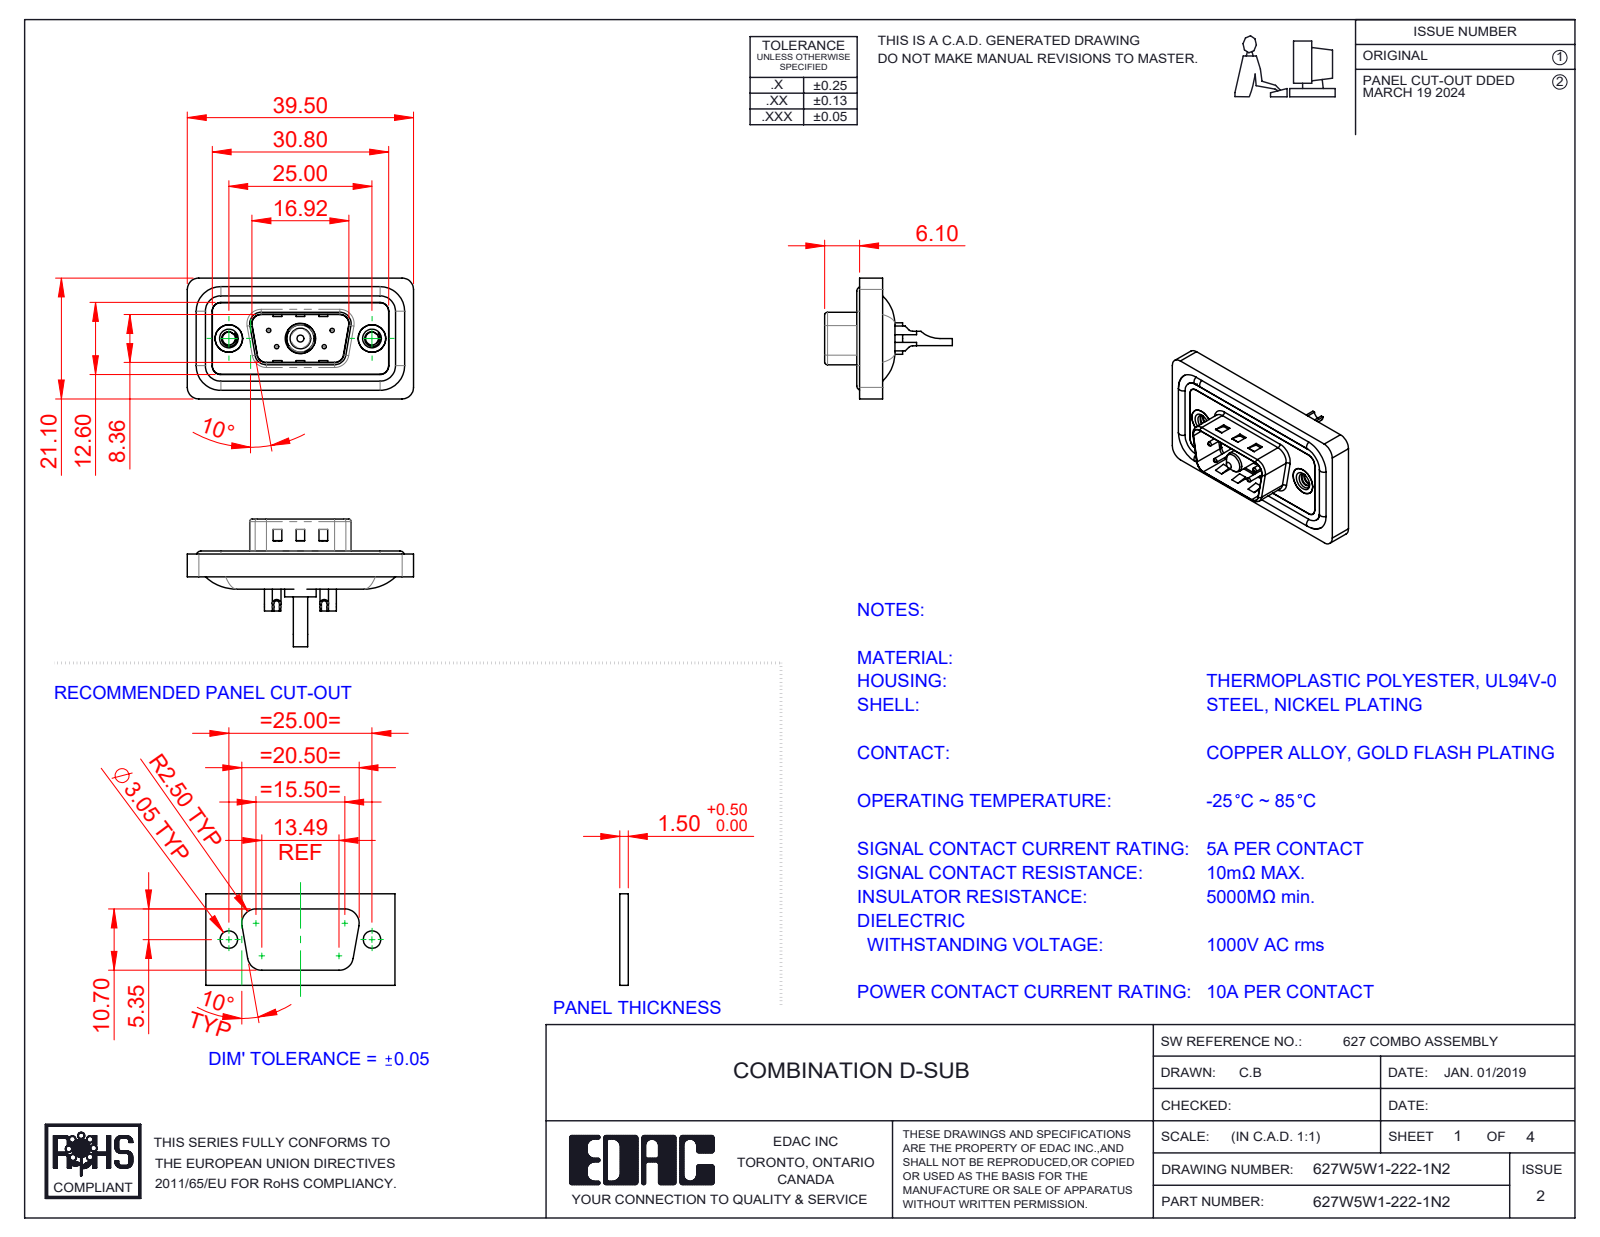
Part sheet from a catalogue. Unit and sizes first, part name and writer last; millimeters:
Units: millimetres
Overall size (bounding box): 39.5 × 22.3 × 21.1
Round holes (diameter × count): ⌀0.75 ×4, ⌀1 ×4, ⌀1.6 ×4, ⌀2 ×4, ⌀2.26 ×2, ⌀4 ×2, ⌀4.8 ×2, ⌀5 ×2, ⌀1.7 ×1, ⌀4.85 ×1, ⌀5.3 ×1
Round bosses / shafts (diameter × count): ⌀1.6 ×4, ⌀1.5 ×4, ⌀4.9 ×2, ⌀5.5 ×1, ⌀5.2 ×1, ⌀4.75 ×1, ⌀3.75 ×1, ⌀3.6 ×1
Partial cylindrical surfaces — rounded edges, fillets, slot ends (radius × count): R1.5 ×22, R2 ×18, R0.5 ×8, R1.6 ×8, R1 ×6, R0.25 ×4, R0.6 ×4, R0.65 ×4
Main face-to-face distances: 0.4, 1.1, 2.9, 1.6, 1.5, 3.1, 0.5, 2.5, 4, 0.8
Hole centre spacings: 3.16, 5.72, 7.1, 12.5, 18.1, 4.39, 4.4, 8.31
Volume: 4 391 mm³ · Surface area: 7 021 mm²
Bodies: 13 solids, 604 faces (193 planar, 266 cylindrical, 145 other)
Part name (STEP PRODUCT): 627Combo Threaded Rivet_2; 627W5W1-222-1N2; 627Combo Shell Rear_09 Contacts; 627Combo Contact Row 2_22 (+5 more)
STEP written by: SolidWorks 2023 (CONFIG_CONTROL_DESIGN)
